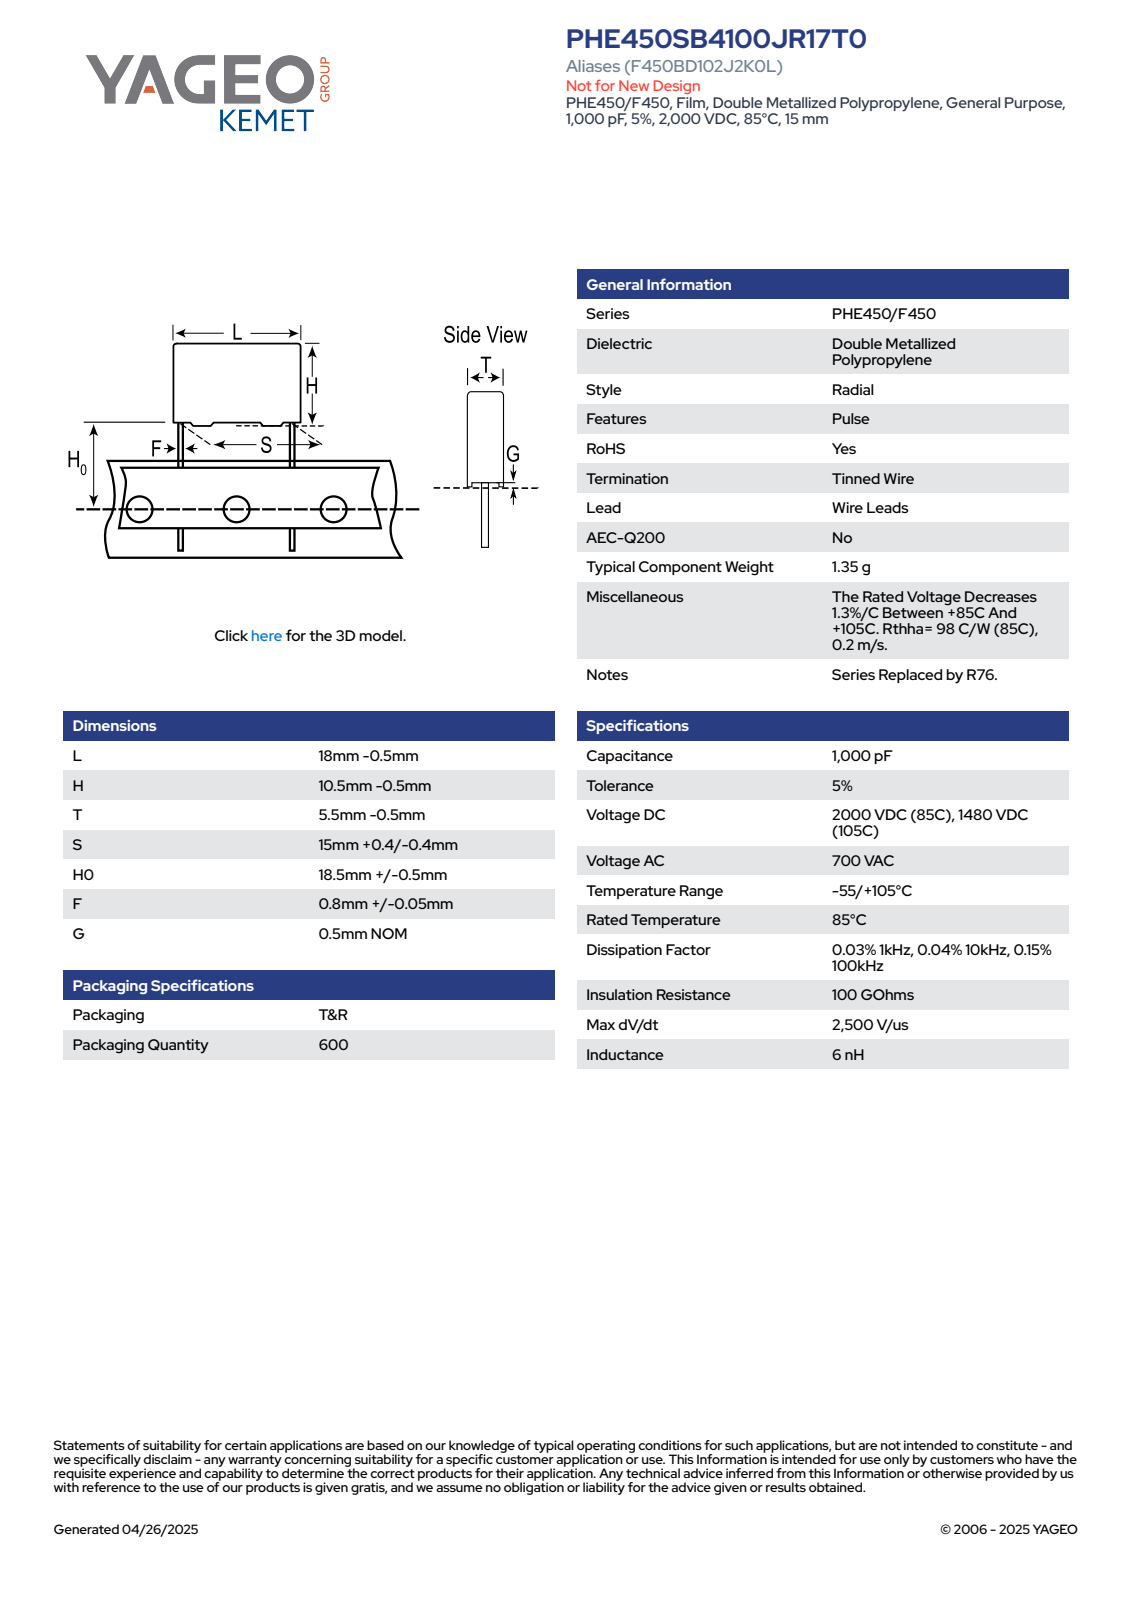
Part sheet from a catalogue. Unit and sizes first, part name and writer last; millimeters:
Units: millimetres
Overall size (bounding box): 29 × 17.5 × 5
Round bosses / shafts (diameter × count): ⌀0.85 ×2
Partial cylindrical surfaces — rounded edges, fillets, slot ends (radius × count): R0.5 ×4
Main face-to-face distances: 5, 9.5, 17.5, 0.5, 10, 4.72, 4.43, 4.71, 19, 19.5
Volume: 853 mm³ · Surface area: 742 mm²
Bodies: 4 solids, 89 faces (81 planar, 8 cylindrical, 0 other)
Part name (STEP PRODUCT): CFR_RBG_18X10.5X5.5_L17.5H10T5S15H019F0.85G0.5
STEP written by: SolidWorks 2014 (AUTOMOTIVE_DESIGN)
